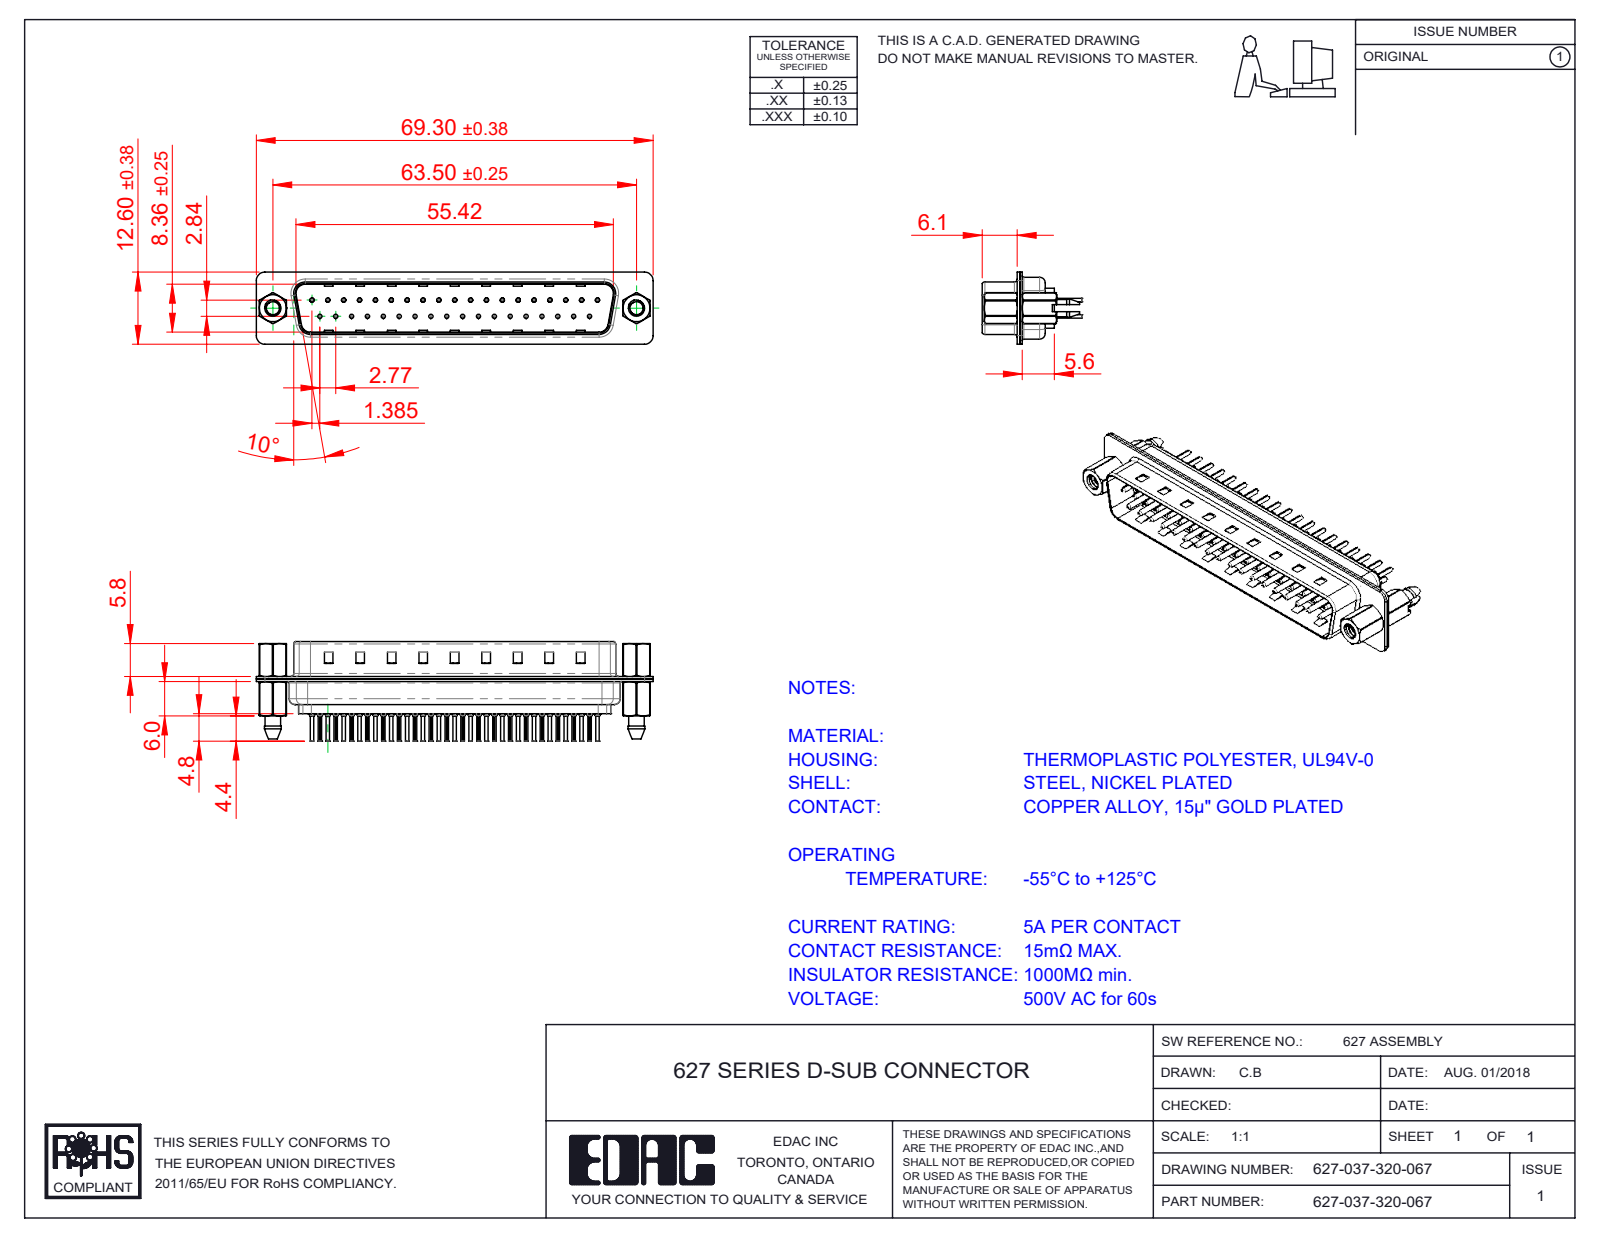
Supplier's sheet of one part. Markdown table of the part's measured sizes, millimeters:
| quantity | value |
| --- | --- |
| part name | 627 4-40 Hex Standoff; 627 Housing_37 LP; 627 Shell Rear_37 Contacts; 627 Shell Front_37 Contacts (+4 more) |
| STEP written by | SolidWorks 2020 (CONFIG_CONTROL_DESIGN) |
| units | millimeters |
| bodies | 44 solids, 4238 faces (1145 planar, 1614 cylindrical, 1479 other) |
| overall size | 69.3 × 17.3 × 12.6 |
| volume | 4 028 mm³ |
| surface area | 11 455 mm² |
| round holes (diameter × count) | 0.2 × 37, 0.35 × 37, 1.1 × 37, 1.6 × 37, 2.26 × 2, 2.29 × 2, 4 × 2, 4.8 × 2 |
| round bosses / shafts (diameter × count) | 2 × 37, 1.5 × 37, 0.75 × 37, 0.6 × 37, 4.9 × 2, 2.79 × 2 |
| partial cylindrical surfaces (radius × count) | 0.1 × 74, 1.5 × 18, 2 × 12, 1.6 × 10, 0.5 × 8, 0.25 × 4, 0.6 × 4, 0.65 × 4 |
| main face-to-face distances | 0.4, 0.82, 9.58, 0.45, 8.76, 1.5, 0.9, 1.4, 6.5, 6.05 |
| hole center spacings | 3.16, 2.77, 5.54, 8.31, 5.04, 10.1, 11.08, 12.78 |
